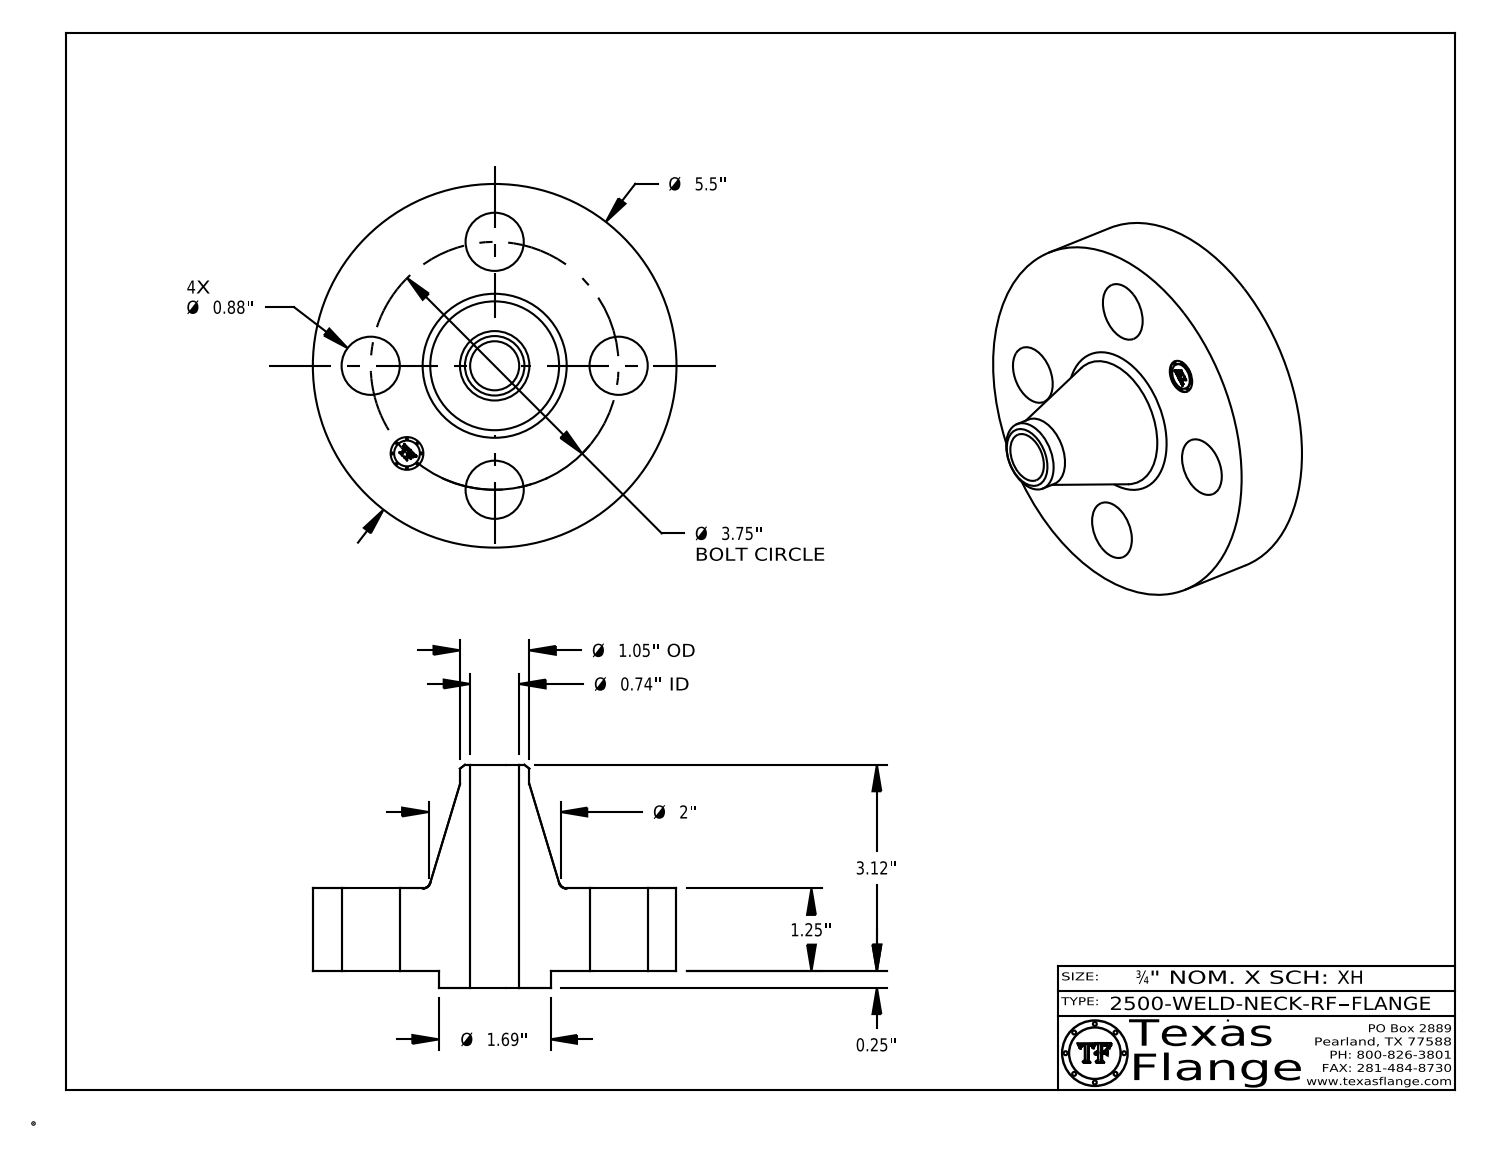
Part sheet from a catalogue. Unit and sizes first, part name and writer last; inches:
Units: inches
Overall size (bounding box): 5.5 × 5.5 × 3.37
Round holes (diameter × count): ⌀0.88 ×4, ⌀0.495 ×1, ⌀0.742 ×1
Round bosses / shafts (diameter × count): ⌀0.03 ×8, ⌀5.5 ×1, ⌀1.69 ×1, ⌀1.05 ×1, ⌀0.39 ×1
Main face-to-face distances: 1.25, 0.25, 1.5, 3.37, 3.12, 1.87, 1.485, 1.235, 0.015, 1.885
Hole centre spacings: 1.875, 2.652, 1.435, 3.465, 3.75
Volume: 28.99 in³ · Surface area: 92.78 in²
Bodies: 1 solid, 411 faces (369 planar, 36 cylindrical, 6 other)
Part name (STEP PRODUCT): 2500-WELD-NECK-RF
STEP written by: CATIA V5 STEP AP214 (AUTOMOTIVE_DESIGN)
